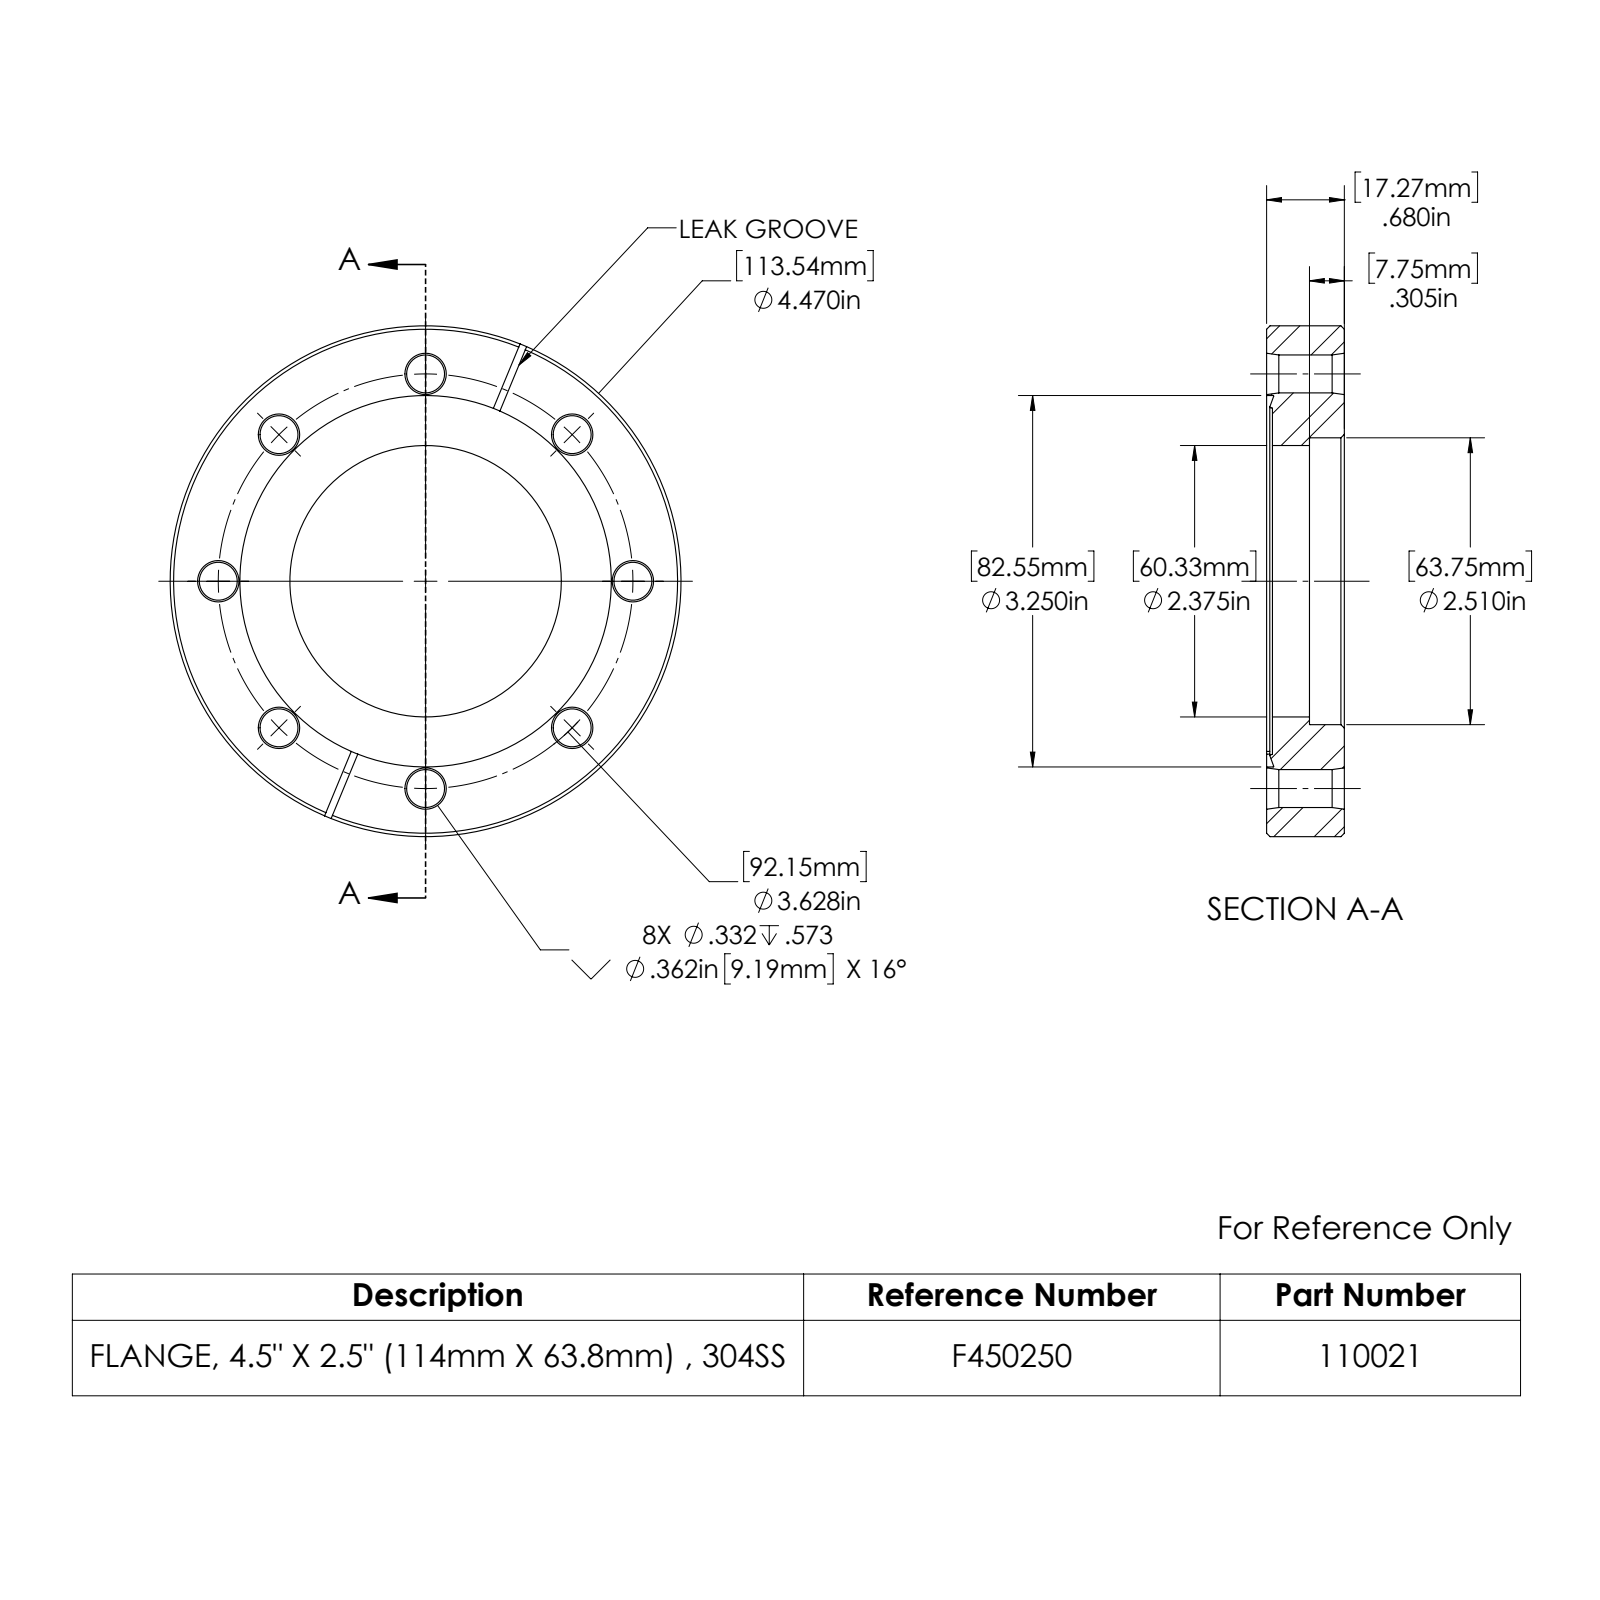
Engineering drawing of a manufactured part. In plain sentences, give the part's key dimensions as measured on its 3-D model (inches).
The part is named "110021". Its 3-D file was written by "SolidWorks 2022 (AUTOMOTIVE_DESIGN)". It is 1 solid with 86 faces: 11 planar, 24 cylindrical and 51 other. Overall it measures 4.47 by 4.47 by 0.68 inches. Its volume is 6.805 cubic inches and its surface area 41.32 square inches. Round holes: 8 of diameter 0.332, 1 of diameter 2.375, 1 of diameter 2.51, 1 of diameter 3.25. Round bosses or shafts: 1 of diameter 4.47. The main face-to-face distances are 0.68, 0.051, 0.629, 0.375, 0.324, 0.305, 0.052, 0.323, 0.628, 0.062. The hole center spacings are 1.389, 1.814, 3.352, 2.565, 2.566, 3.628, 3.628.
